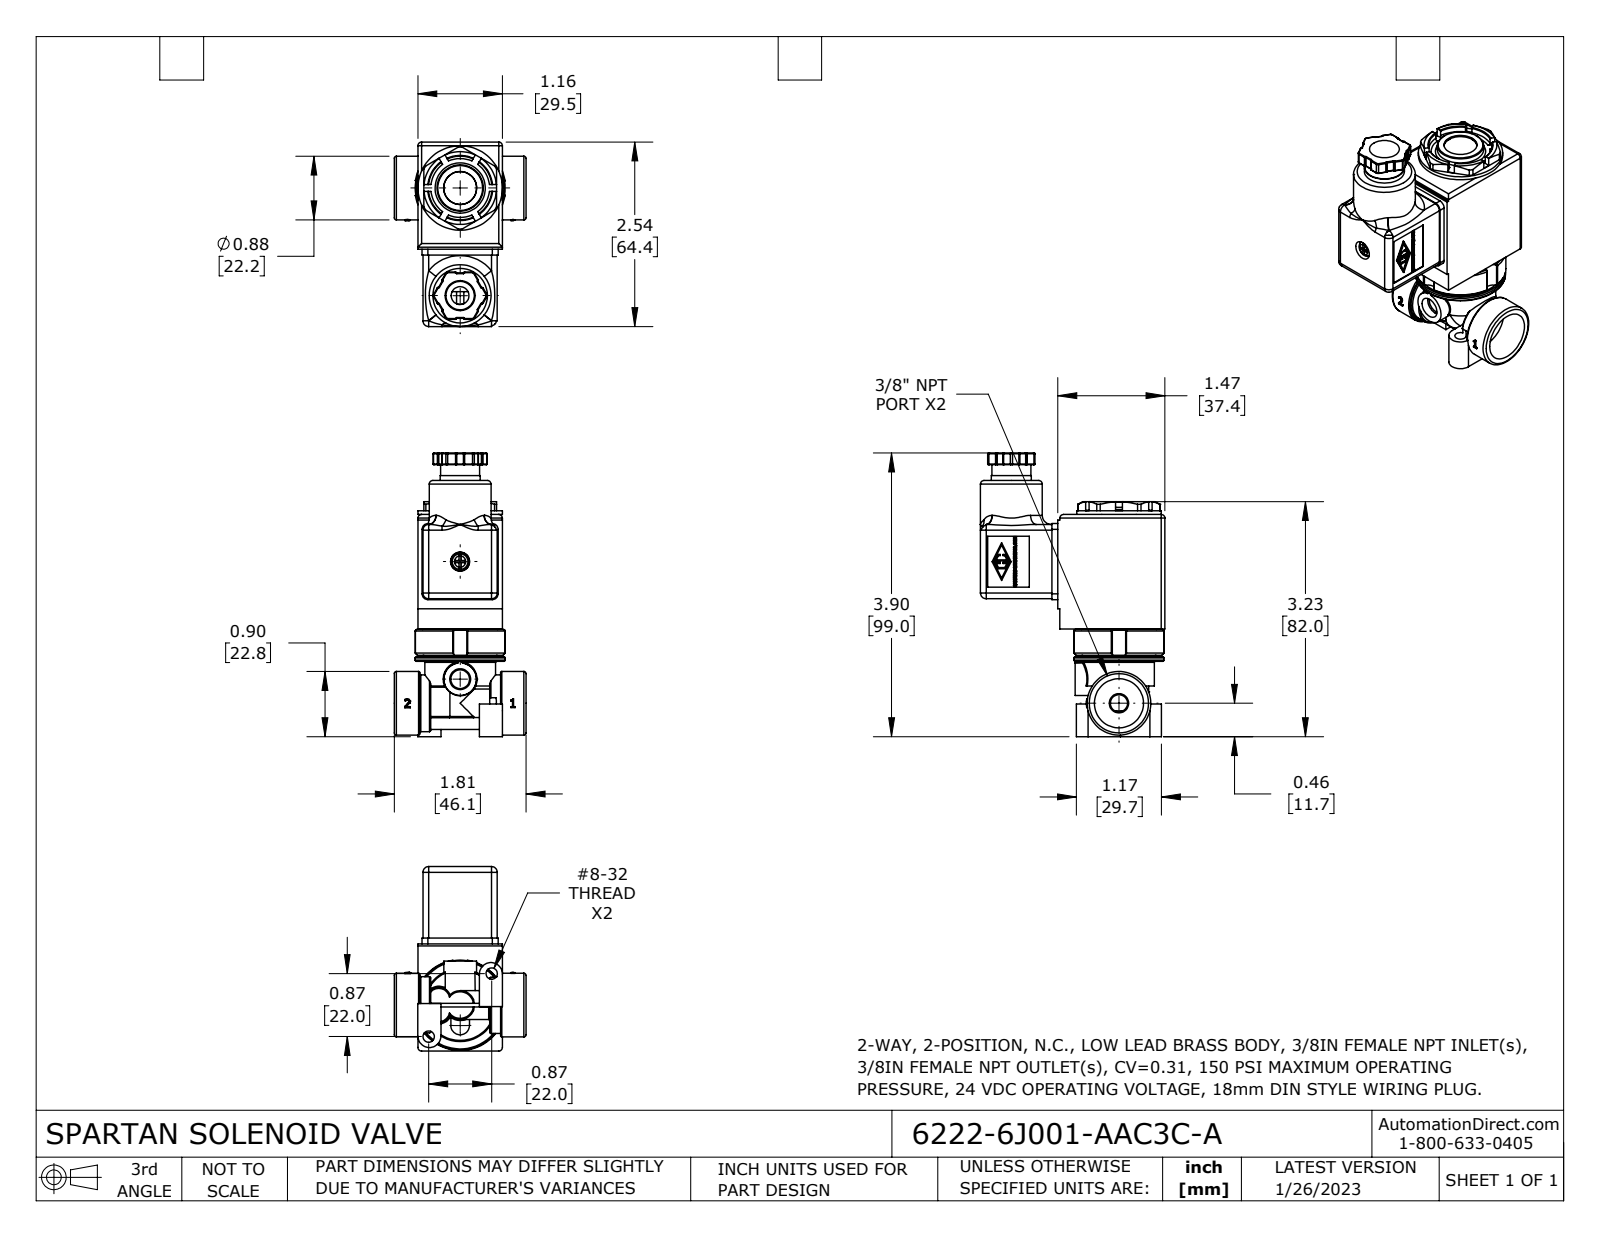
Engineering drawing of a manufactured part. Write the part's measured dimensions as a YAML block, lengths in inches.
part_name: "6222-6J001-AAC3C-A"
step_written_by: "SolidWorks 2021 (CONFIG_CONTROL_DESIGN)"
units: inches
bodies: {solids: 4, faces: 1617, planar: 787, cylindrical: 283, other: 547}
overall_size: [3.898, 2.536, 1.813]
volume: 4.308
surface_area: 57.59
round_holes:
  - {diameter: 0.156, count: 2}
  - {diameter: 0.236, count: 2}
  - {diameter: 0.053, count: 1}
  - {diameter: 0.06, count: 1}
  - {diameter: 0.093, count: 1}
  - {diameter: 0.102, count: 1}
  - {diameter: 0.12, count: 1}
  - {diameter: 0.203, count: 1}
  - {diameter: 0.245, count: 1}
  - {diameter: 0.263, count: 1}
  - {diameter: 0.287, count: 1}
  - {diameter: 0.39, count: 1}
round_bosses_or_shafts:
  - {diameter: 1.236, count: 1}
  - {diameter: 1.16, count: 1}
  - {diameter: 1, count: 1}
  - {diameter: 0.972, count: 1}
  - {diameter: 0.875, count: 1}
  - {diameter: 0.85, count: 1}
  - {diameter: 0.78, count: 1}
  - {diameter: 0.636, count: 1}
partial_cylinders:
  - {radius: 0.01, count: 56}
  - {radius: 0.05, count: 14}
  - {radius: 0.08, count: 12}
  - {radius: 0.03, count: 6}
  - {radius: 0.008, count: 4}
  - {radius: 0.02, count: 4}
  - {radius: 0.04, count: 4}
  - {radius: 0.094, count: 4}
face_to_face_distances: [1.161, 0.925, 1.472, 0.039, 0.917, 0.048, 0.973, 0.079, 1.043, 0.119]
hole_center_spacings: [0.613, 0.281, 0.352, 0.459, 0.819, 0.835, 1.127, 1.132]
